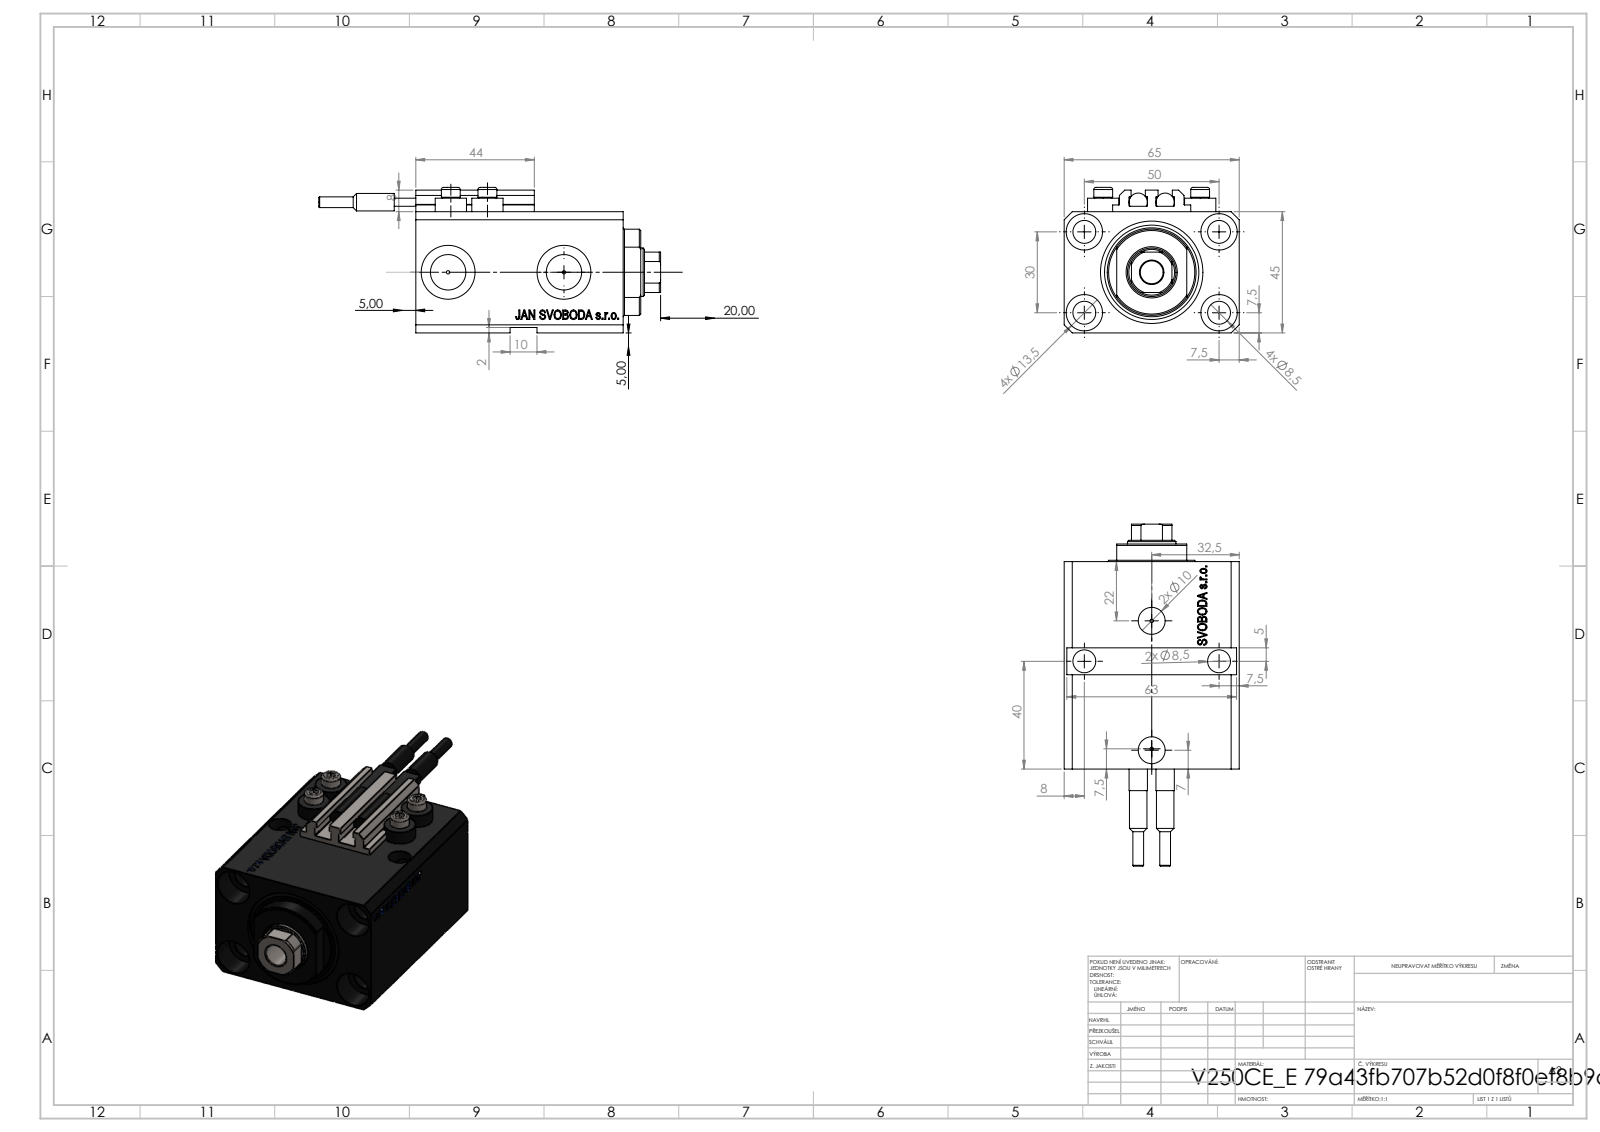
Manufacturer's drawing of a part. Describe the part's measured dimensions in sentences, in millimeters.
The part is named "V250CE_E_Body; V250CE_C_VCP; V250CE_VC_E; ALLEN BOLT V250CE (+1 more)". Its 3-D file was written by "SolidWorks 2019 (CONFIG_CONTROL_DESIGN)". It is 10 solids with 1119 faces: 543 planar, 138 cylindrical and 438 other. Overall it measures 127 by 65 by 54 millimeters. Its volume is 203 348 cubic millimeters and its surface area 61 935 square millimeters. Round holes: 7 of diameter 8.5, 4 of diameter 1.25, 4 of diameter 4, 4 of diameter 13.5, 2 of diameter 10, 2 of diameter 13.16, 2 of diameter 20, 1 of diameter 18, 1 of diameter 25, 1 of diameter 38. Round bosses or shafts: 4 of diameter 11.6, 4 of diameter 7, 2 of diameter 6.8, 2 of diameter 6.5, 2 of diameter 4. Partial cylindrical surfaces (rounded edges, fillets, slot ends): 10 of radius 0.2, 1 of radius 8.5, 1 of radius 16. The main face-to-face distances are 45, 65, 63, 2, 14, 3, 77, 47, 5, 6.9. The hole center spacings are 29.15, 50, 13.6, 15.12, 18.81, 18.97, 26.22, 26.61.
